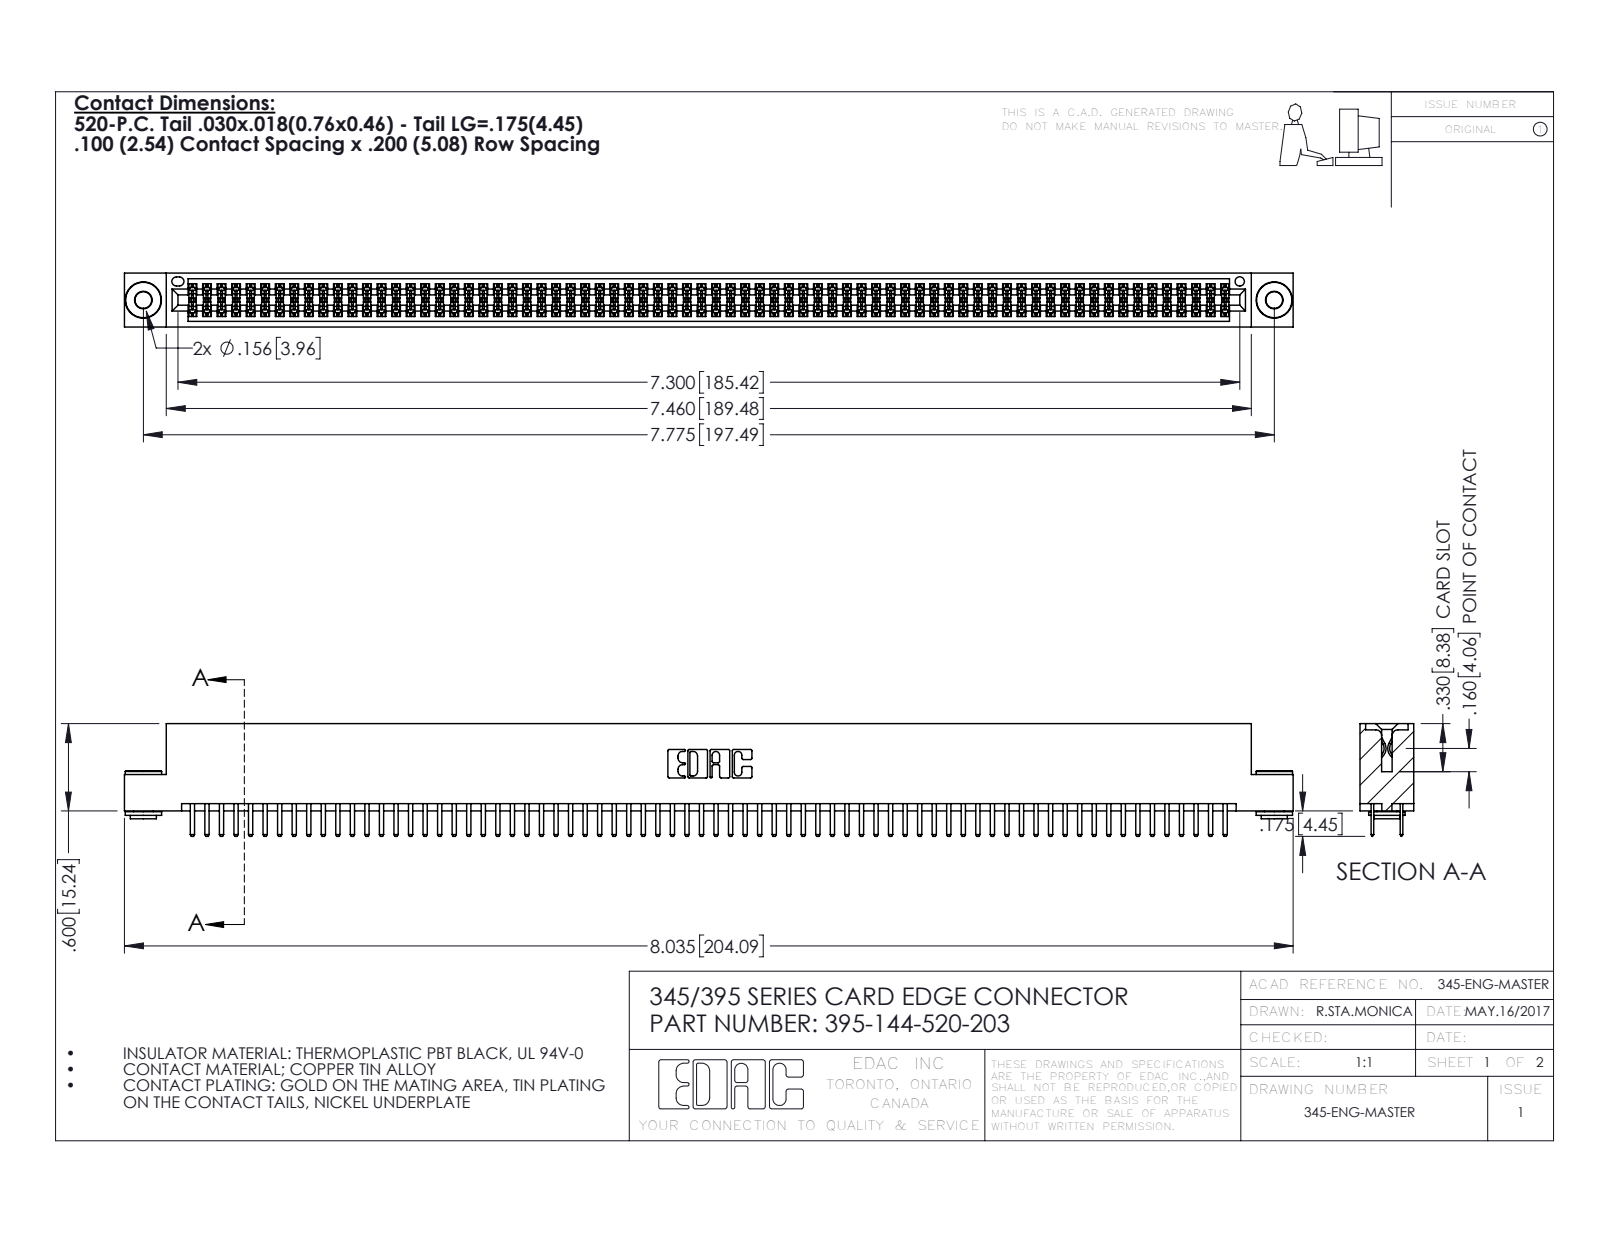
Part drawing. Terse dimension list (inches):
name: 395-144-520-203; 345-292-001_345-293-120; 345-250-002_345-250-002-102; 345 Part_Flush Mounting Lugs - 0.156 Dia-TH
written by: SolidWorks 2016 (CONFIG_CONTROL_DESIGN)
unit: in
bodies: 147 solids, 7940 faces (5130 planar, 2802 cylindrical, 8 other)
size: 8.035 × 0.775 × 0.37
volume: 1.224 in³; area: 46.97 in²
holes: 2× ⌀0.116, 2× ⌀0.156, 1× ⌀0.064
bosses: 2× ⌀0.25, 2× ⌀0.18, 2× ⌀0.136
rounds: 216× R0.006, 148× R0.01, 22× R0.01, 6× R0.007, 6× R0.031, 3× R0.026, 2× R0.014, 2× R0.019
face distances: 0.072, 0.298, 0.2, 0.37, 0.025, 0.098, 0.272, 0.225, 0.022, 0.072
hole spacings: 0.27, 7.539, 7.775
